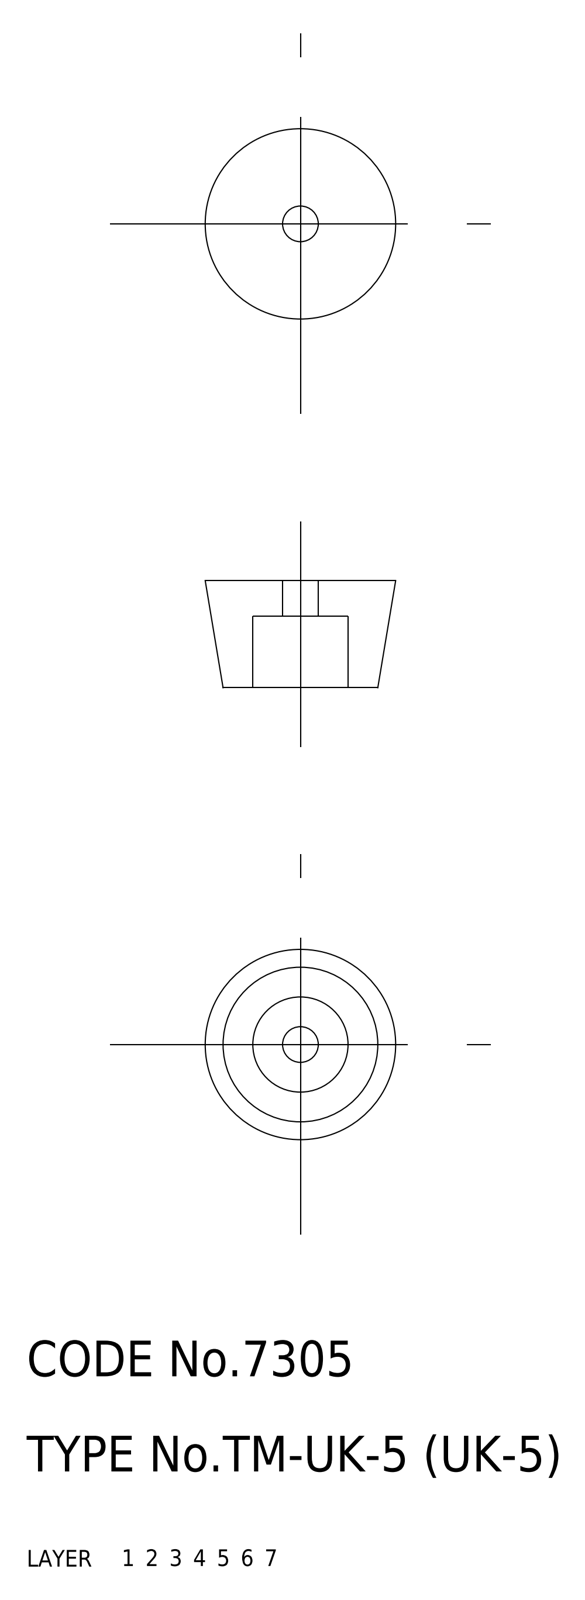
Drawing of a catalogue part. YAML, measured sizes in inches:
part_name: "washer; rubber foot; UK_5_10876_36"
step_written_by: "CADfix (AUTOMOTIVE_DESIGN)"
units: inches
bodies: {solids: 2, faces: 21, planar: 0, cylindrical: 0, other: 21}
overall_size: [0.63, 0.63, 0.354]
volume: 0.071
surface_area: 1.804
